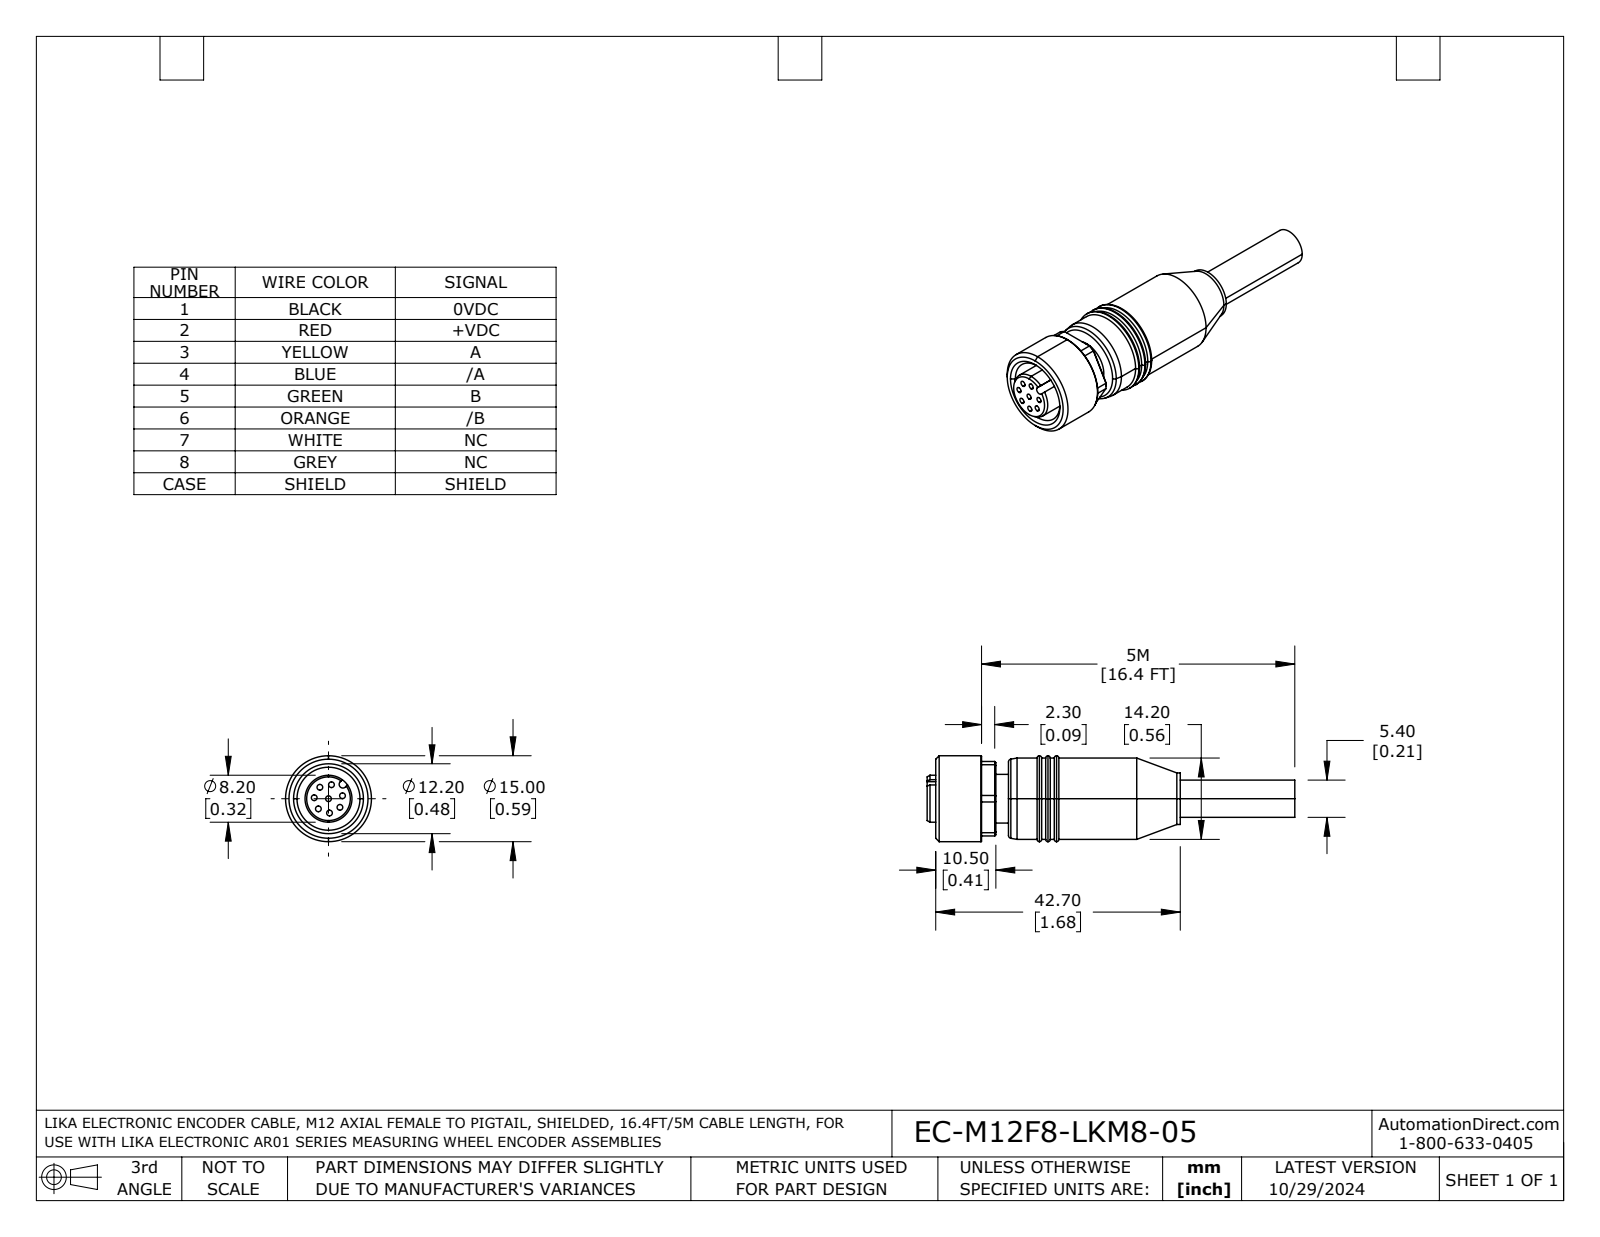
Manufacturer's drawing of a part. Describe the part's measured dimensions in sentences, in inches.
The part is named "EC-M12F8-LKM8-05". Its 3-D file was written by "SolidWorks 2021 (AUTOMOTIVE_DESIGN)". It is 1 solid with 113 faces: 31 planar, 43 cylindrical and 39 other. Overall it measures 2.528 by 0.591 by 0.591 inches. Its volume is 0.404 cubic inches and its surface area 5.26 square inches. Round holes: 8 of diameter 0.039, 1 of diameter 0.433. Round bosses or shafts: 1 of diameter 0.591, 1 of diameter 0.559, 1 of diameter 0.354, 1 of diameter 0.335, 1 of diameter 0.323, 1 of diameter 0.256. Partial cylindrical surfaces (rounded edges, fillets, slot ends): 1 of radius 0.026, 1 of radius 0.283. The main face-to-face distances are 0.087, 0.512, 0.205, 0.118, 0.559, 0.472, 0.354, 1.969, 2.055, 2.173. The hole center spacings are 0.098, 0.081, 0.149, 0.195, 0.082, 0.166, 0.189, 0.189.
